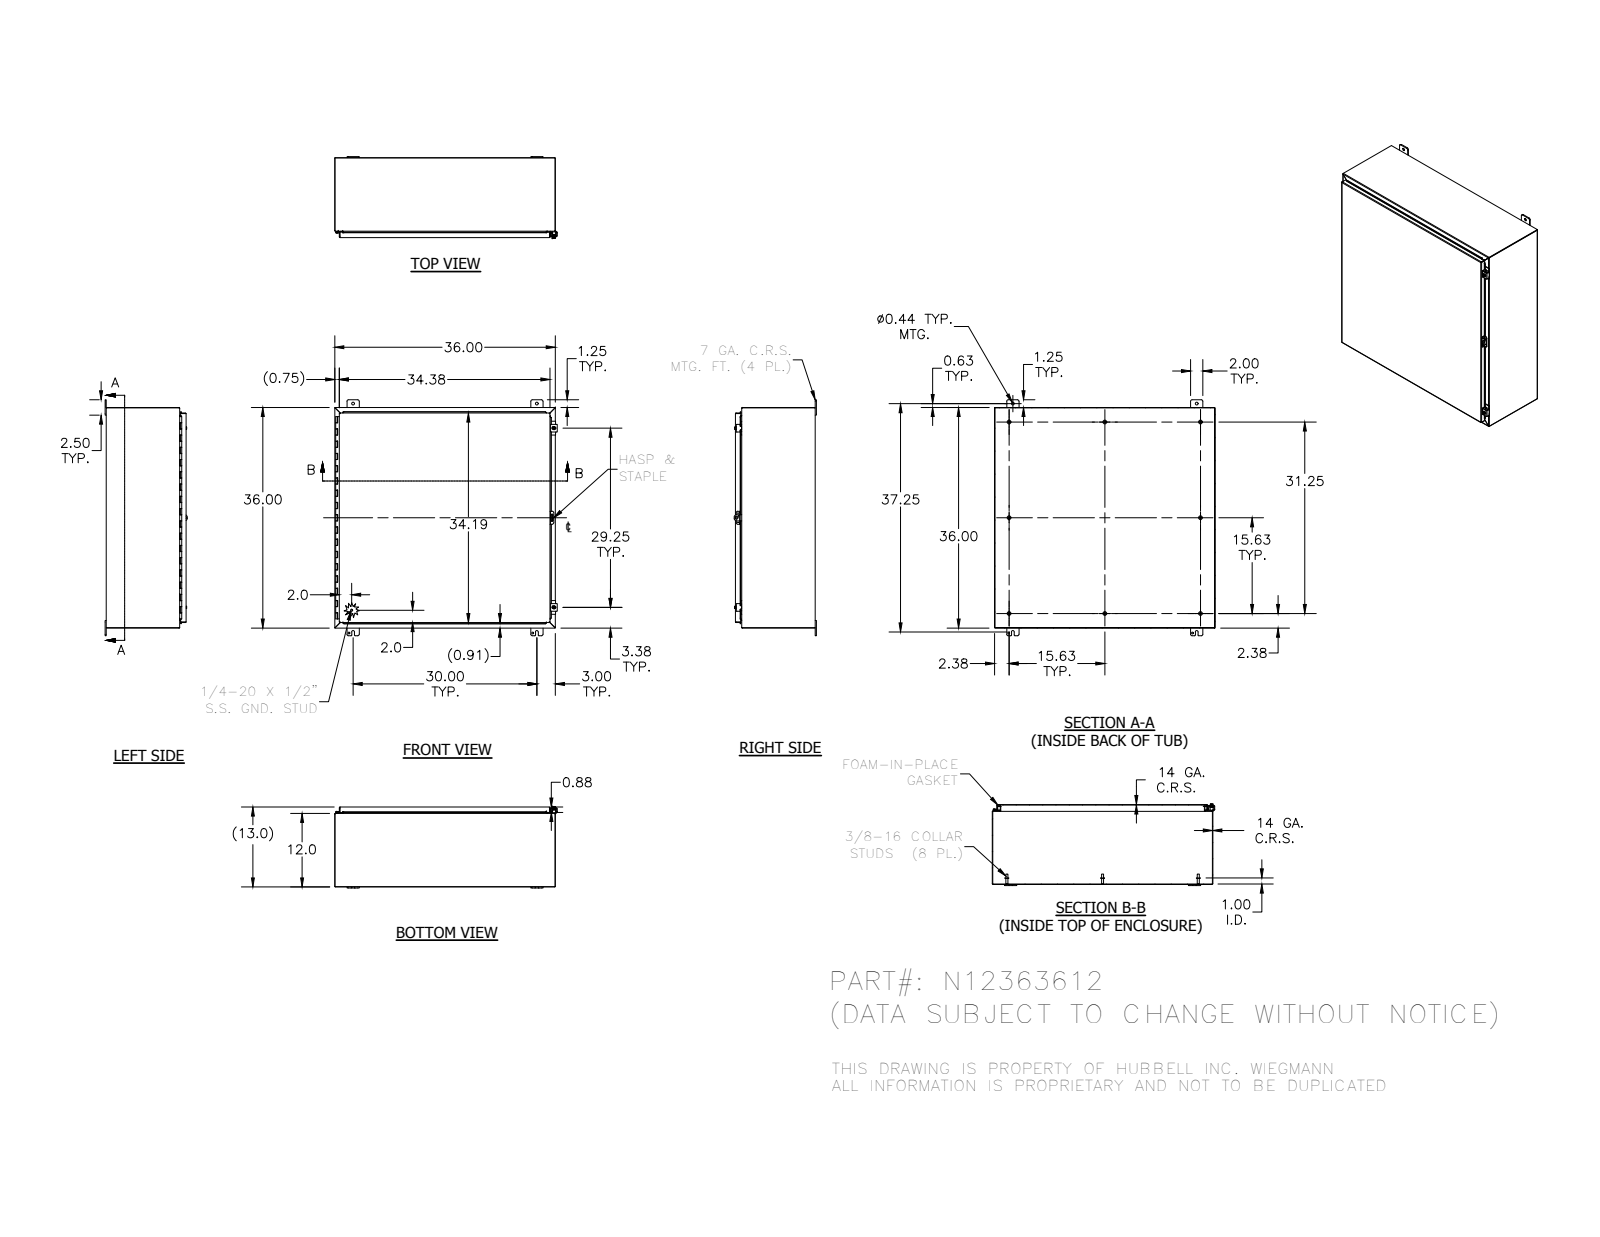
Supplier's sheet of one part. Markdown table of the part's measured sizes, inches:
| quantity | value |
| --- | --- |
| part name | N12363612; 34840; 38413; N123612TB (+8 more) |
| STEP written by | Autodesk Inventor 2012 (AUTOMOTIVE_DESIGN) |
| units | inches |
| bodies | 33 solids, 998 faces (589 planar, 304 cylindrical, 105 other) |
| overall size | 38.5 × 36.311 × 13.41 |
| volume | 366.2 in³ |
| surface area | 9 684 in² |
| round holes (diameter × count) | 0.313 × 4, 0.438 × 4, 0.11 × 3, 0.211 × 2, 0.281 × 2, 0.3 × 2, 0.125 × 1, 0.156 × 1, 0.5 × 1 |
| round bosses / shafts (diameter × count) | 0.625 × 8, 0.33 × 8, 0.25 × 4, 0.52 × 2, 0.5 × 2, 0.35 × 2, 0.115 × 2, 0.337 × 1 |
| partial cylindrical surfaces (radius × count) | 0.03 × 27, 0.125 × 25, 0.25 × 25, 0.031 × 21, 0.105 × 21, 0.063 × 13, 0.1 × 4, 0.141 × 4 |
| main face-to-face distances | 0.074, 12.959, 35.926, 12.885, 13.033, 35.852, 36, 11.926, 1.033, 12 |
| hole center spacings | 1.593, 30, 36, 46.861, 0.791, 29.348, 30.72, 34.57 |
